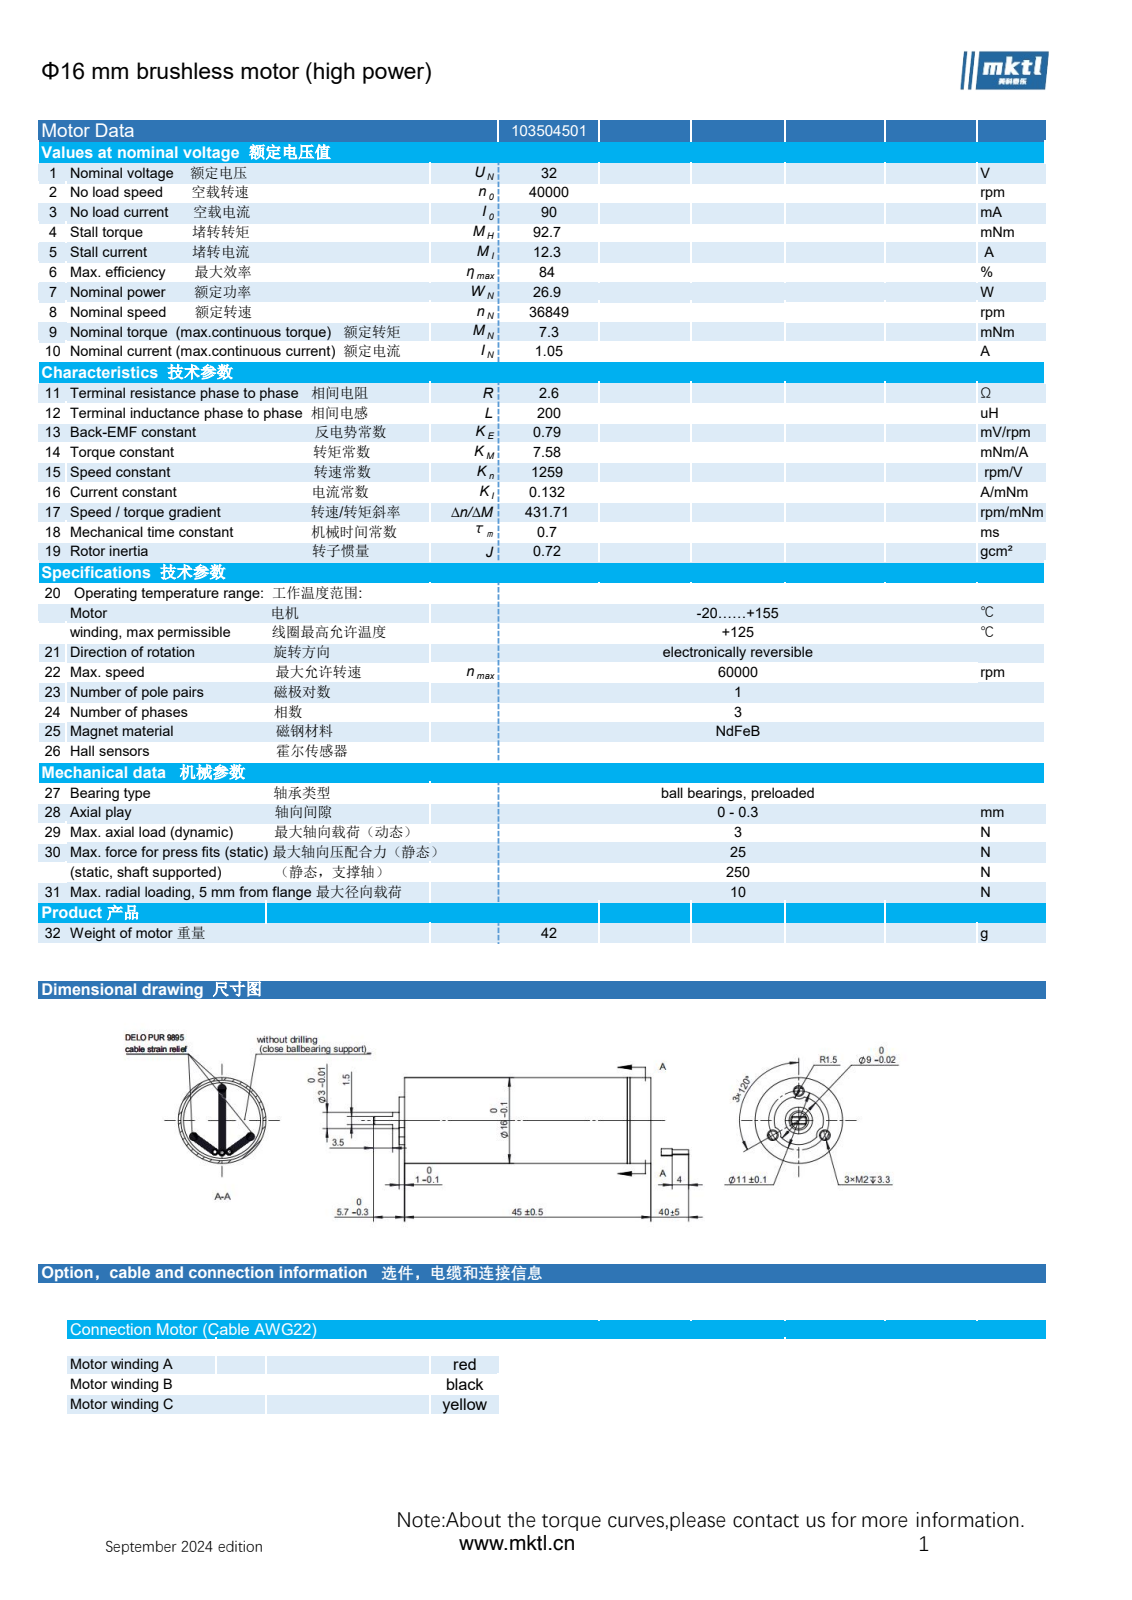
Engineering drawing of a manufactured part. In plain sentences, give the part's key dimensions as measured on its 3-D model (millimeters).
The part is named "approval 103504501". Its 3-D file was written by "SolidWorks 2018 (CONFIG_CONTROL_DESIGN)". It is 169 solids with 1197 faces: 370 planar, 767 cylindrical and 60 other. Overall it measures 57.6 by 16 by 16 millimeters. Its volume is 7 875 cubic millimeters and its surface area 36 250 square millimeters. Round holes: 3 of diameter 1.5, 3 of diameter 1.6, 1 of diameter 3, 1 of diameter 3.1, 1 of diameter 7, 1 of diameter 8, 1 of diameter 8.1, 1 of diameter 8.8, 1 of diameter 10.8, 1 of diameter 11, 1 of diameter 11.3, 1 of diameter 12. Round bosses or shafts: 3 of diameter 1.2, 3 of diameter 0.8, 3 of diameter 0.3, 1 of diameter 16, 1 of diameter 15, 1 of diameter 14.9, 1 of diameter 7.4, 1 of diameter 7.35. Partial cylindrical surfaces (rounded edges, fillets, slot ends): 12 of radius 0.5, 3 of radius 1.5, 2 of radius 0.8, 1 of radius 4.5, 1 of radius 5.2, 1 of radius 5.75, 1 of radius 6.5, 1 of radius 6.75. The main face-to-face distances are 0.4, 0.6, 0.8, 1, 1.2, 1.4, 1.6, 1.8, 2, 2.2. The hole center spacings are 9.96, 5.5, 6, 9.52, 0.51, 10.39, 0.5, 10.4.
